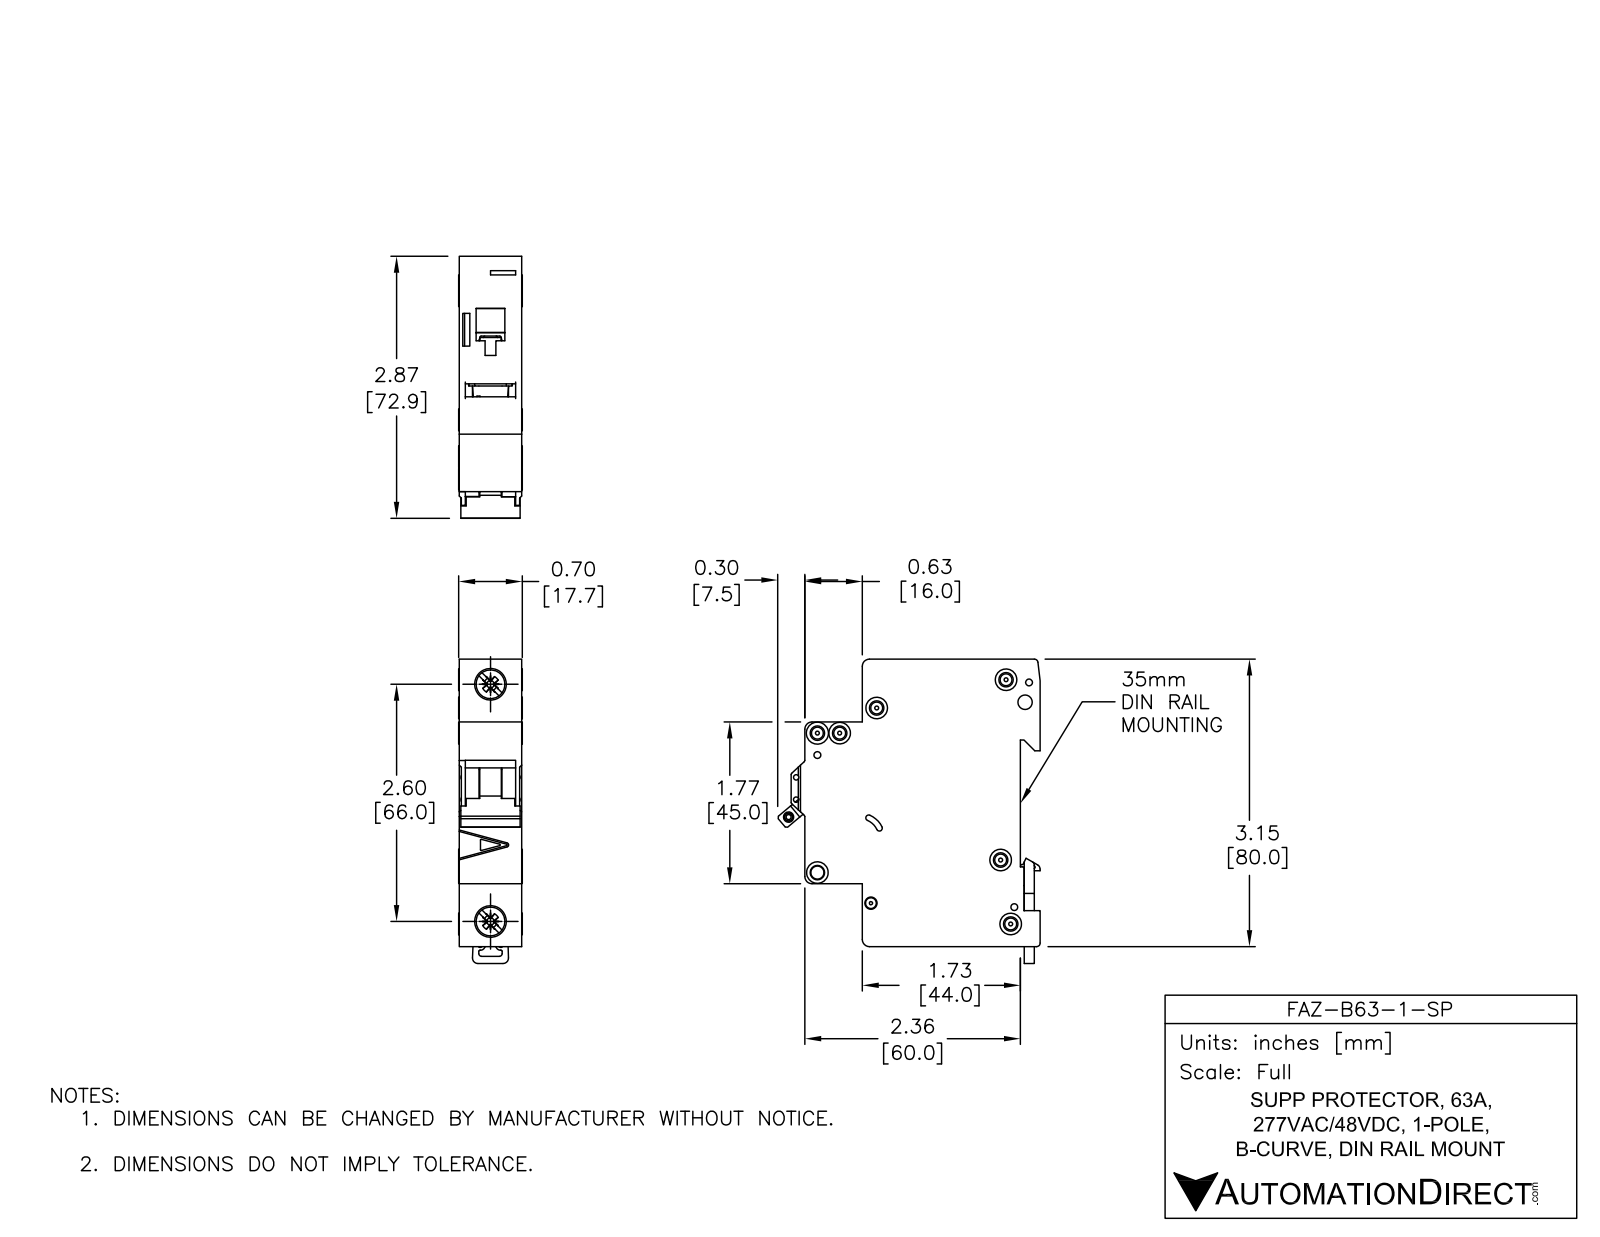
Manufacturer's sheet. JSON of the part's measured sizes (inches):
{"part_name": "FAZ-B63-1-SP", "step_written_by": "SolidWorks 2014 (AUTOMOTIVE_DESIGN)", "units": "inches", "bodies": {"solids": 5, "faces": 558, "planar": 235, "cylindrical": 202, "other": 121}, "overall_size": [3.338, 2.876, 0.697], "volume_in3": 4.573, "surface_area_in2": 30.29, "round_holes": [[0.142, 6], [0.075, 3], [0.043, 2], [0.059, 2], [0.157, 2], [0.281, 2], [0.085, 1], [0.087, 1], [0.1, 1], [0.13, 1], [0.134, 1]], "round_bosses_or_shafts": [[0.236, 4], [0.323, 2], [0.098, 1]], "partial_cylinders_radius": [[0.01, 30], [0.02, 13], [0.079, 8], [0.008, 5], [0.039, 4], [0.031, 2], [0.118, 2], [0.059, 1]], "face_to_face_distances": [0.689, 3.129, 0.217, 1.949, 1.732, 2.579, 2.362, 0.63, 0.069, 0.62], "hole_center_spacings": [0.244, 0.537, 0.189, 0.204, 0.221, 0.24, 0.254, 0.322]}
